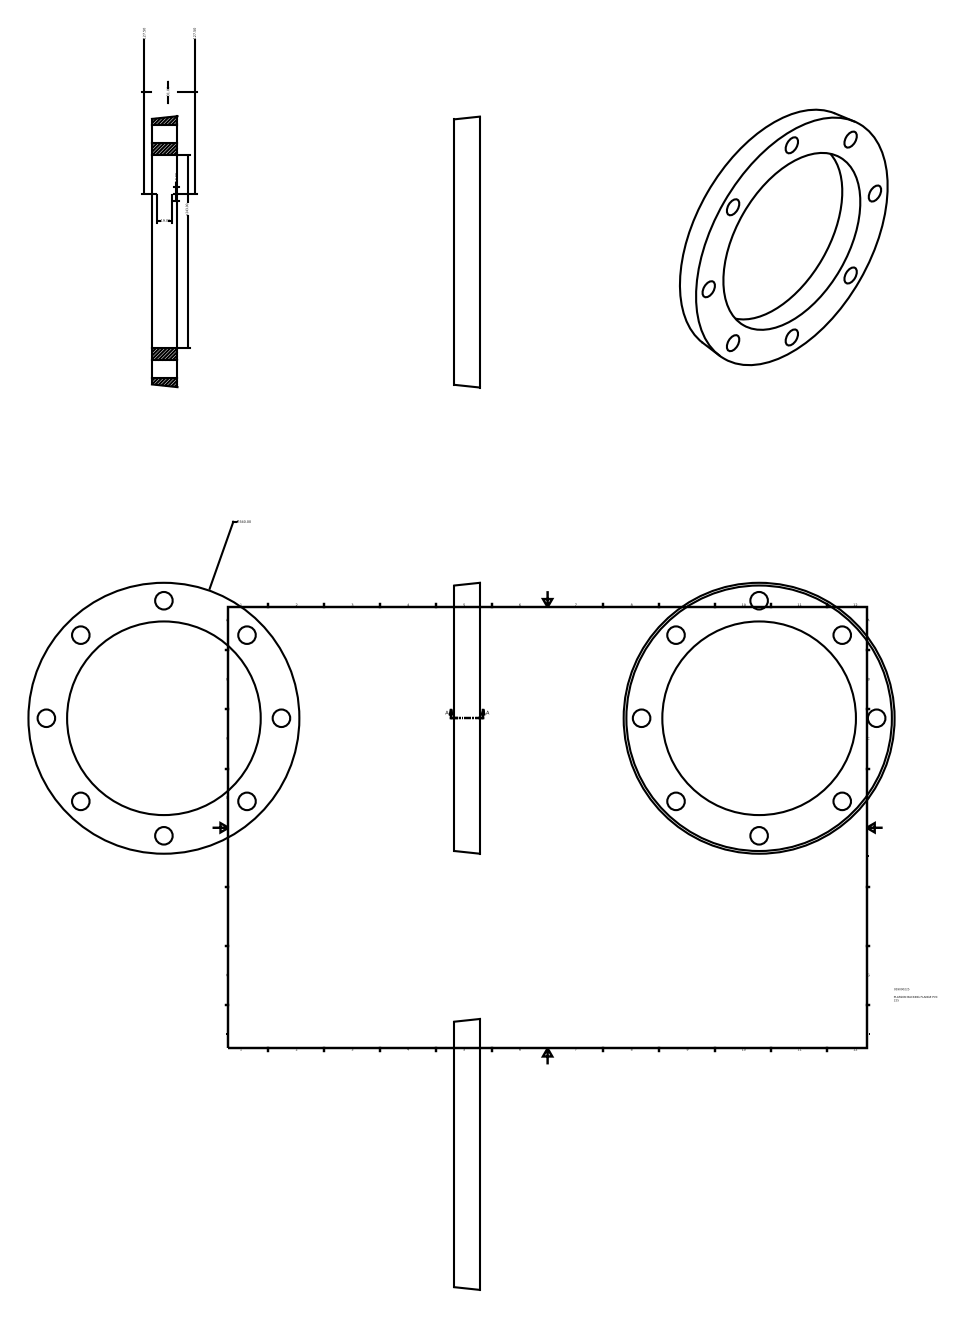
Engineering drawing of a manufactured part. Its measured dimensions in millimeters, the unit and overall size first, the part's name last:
Units: millimetres
Overall size (bounding box): 340 × 340 × 32
Round holes (diameter × count): ⌀22 ×8, ⌀243 ×1
Main face-to-face distances: 32
Hole centre spacings: 112.89, 147.5, 208.6, 272.55, 295
Volume: 1 266 000 mm³ · Surface area: 155 304 mm²
Bodies: 1 solid, 12 faces (2 planar, 9 cylindrical, 1 other)
Part name (STEP PRODUCT): 059000225
STEP written by: Autodesk Inventor 2015 (AUTOMOTIVE_DESIGN)
